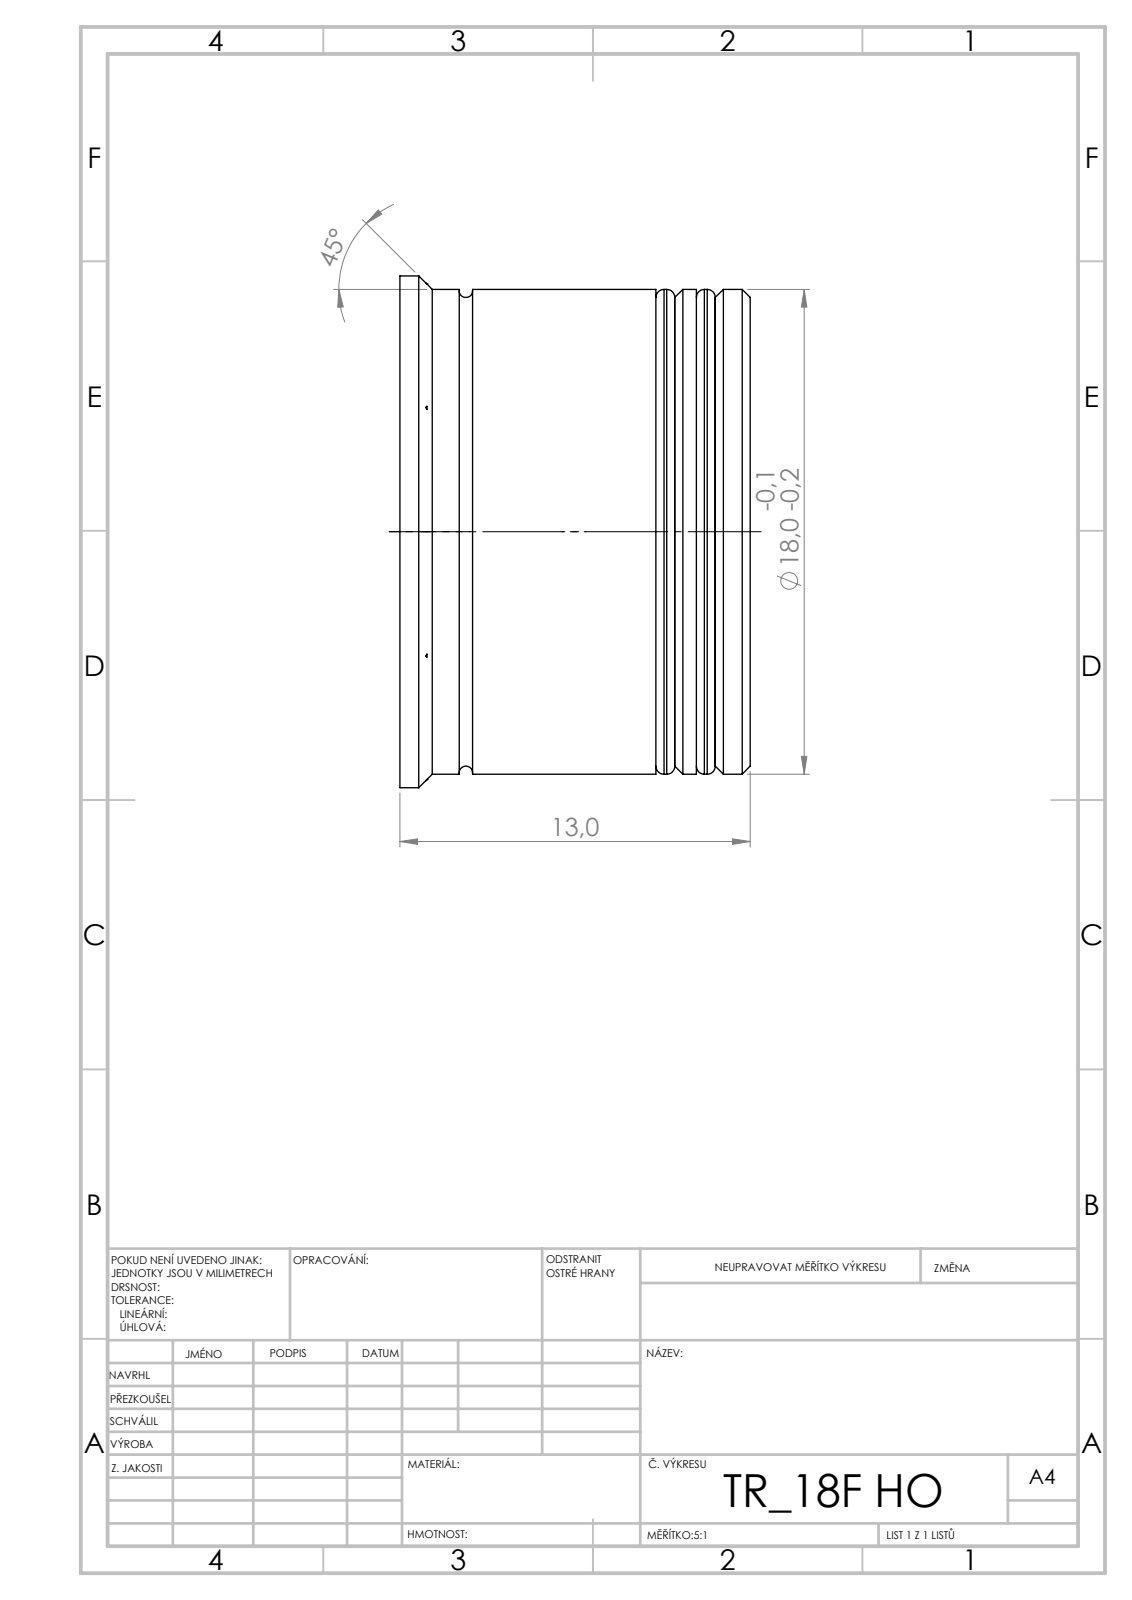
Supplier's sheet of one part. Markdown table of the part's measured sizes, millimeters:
| quantity | value |
| --- | --- |
| STEP written by | SolidWorks 2019 (CONFIG_CONTROL_DESIGN) |
| units | millimeters |
| bodies | 3 solids, 74 faces (29 planar, 25 cylindrical, 20 other) |
| overall size | 19 × 19 × 13 |
| volume | 3 439 mm³ |
| surface area | 2 531 mm² |
| round bosses / shafts (diameter × count) | 19 × 1, 18 × 1, 17.4 × 1 |
| partial cylindrical surfaces (radius × count) | 7.5 × 1 |
| main face-to-face distances | 1.5, 0.7, 2.2, 2, 3.5, 1.3, 2.8, 0.8, 12, 10.7 |
